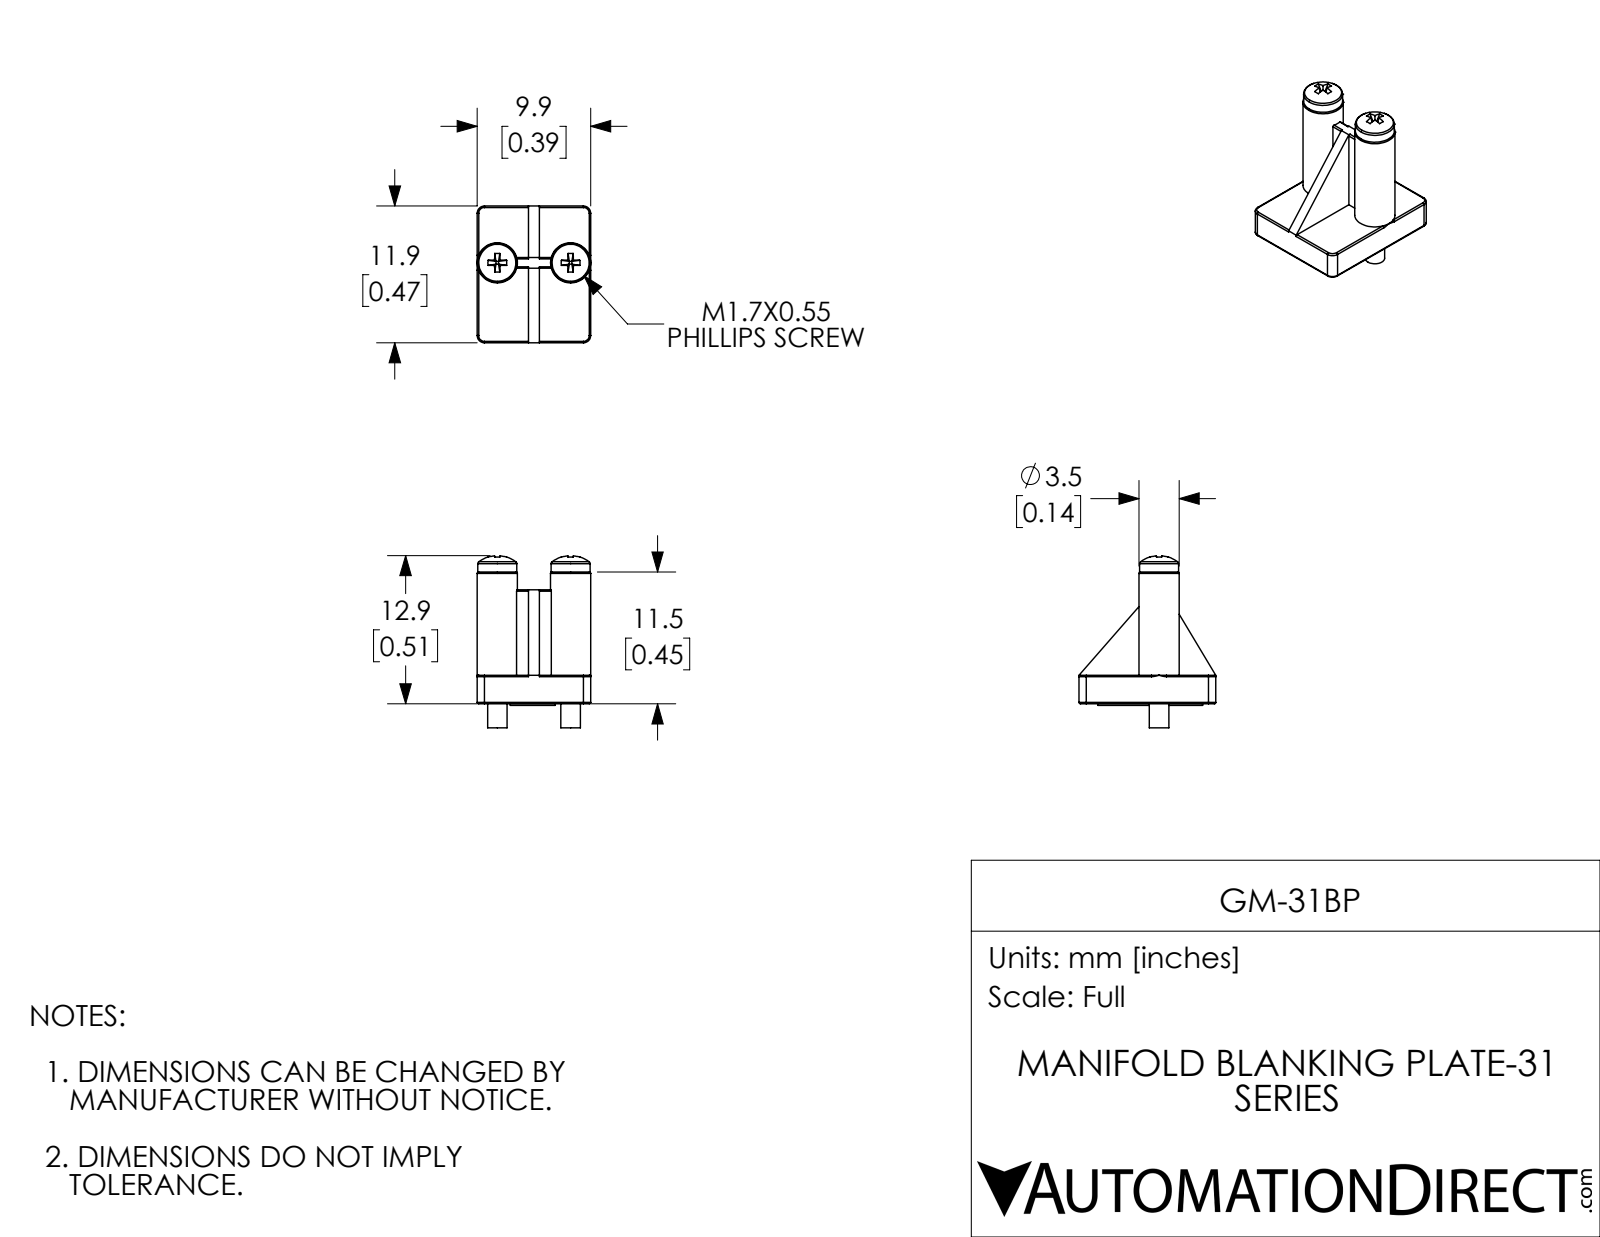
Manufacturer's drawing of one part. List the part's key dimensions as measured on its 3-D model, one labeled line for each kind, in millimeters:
Part name (STEP PRODUCT): GM-31BP
STEP written by: SolidWorks 2018 (AUTOMOTIVE_DESIGN)
Units: millimetres
Bodies: 3 solids, 132 faces (72 planar, 36 cylindrical, 24 other)
Overall size (bounding box): 15 × 11.9 × 9.9
Volume: 540 mm³ · Surface area: 983 mm²
Round holes (diameter × count): ⌀1.9 ×2
Round bosses / shafts (diameter × count): ⌀3.5 ×2, ⌀3.4 ×2, ⌀1.7 ×2
Partial cylindrical surfaces — rounded edges, fillets, slot ends (radius × count): R0.1 ×10, R0.6 ×4
Main face-to-face distances: 2.5, 4.5, 5.4, 0.9, 11.5, 9, 9.9, 11.9, 6.5, 7.5
Hole centre spacings: 6.4
